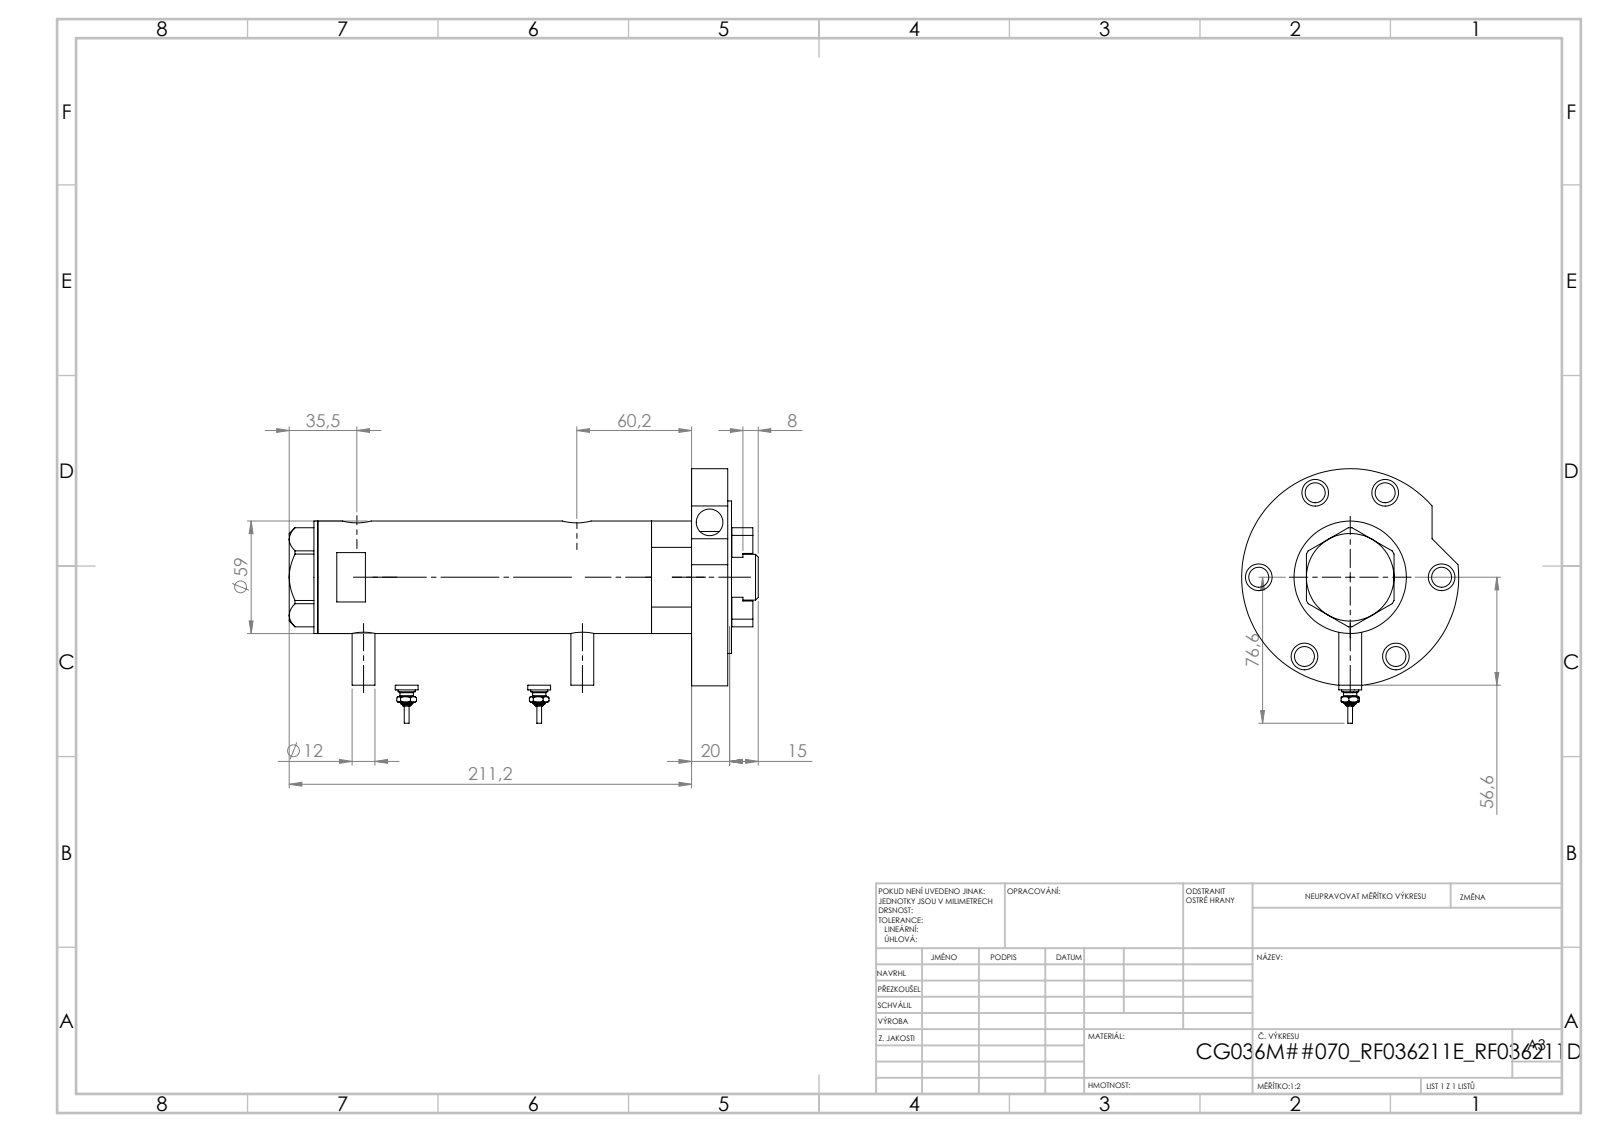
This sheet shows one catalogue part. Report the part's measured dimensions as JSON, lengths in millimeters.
{"part_name": "V270CG_BACK; V270CG_SWITCH; V270CG_FRONT; V270CG_RF211E (+3 more)", "step_written_by": "SolidWorks 2019 (CONFIG_CONTROL_DESIGN)", "units": "millimeters", "bodies": {"solids": 9, "faces": 316, "planar": 116, "cylindrical": 126, "other": 74}, "overall_size": [233.42, 118.8, 114], "volume_mm3": 669932, "surface_area_mm2": 147882, "round_holes": [[10.5, 10], [14, 7], [6.1, 4], [5, 2], [9.73, 2], [12.5, 2], [15, 2], [8.5, 1], [25, 1], [26.5, 1], [36, 1], [40, 1]], "round_bosses_or_shafts": [[12, 4], [9, 2], [7, 2], [4.34, 2], [2.4, 2], [114, 1], [80, 1], [59, 1]], "face_to_face_distances": [19, 2, 201.84, 21, 180.84, 199.84, 127.34, 53.5, 72.5, 74.5], "hole_center_spacings": [48, 19.92, 46.09, 57.24, 2.9, 3.5, 12, 28.22]}
